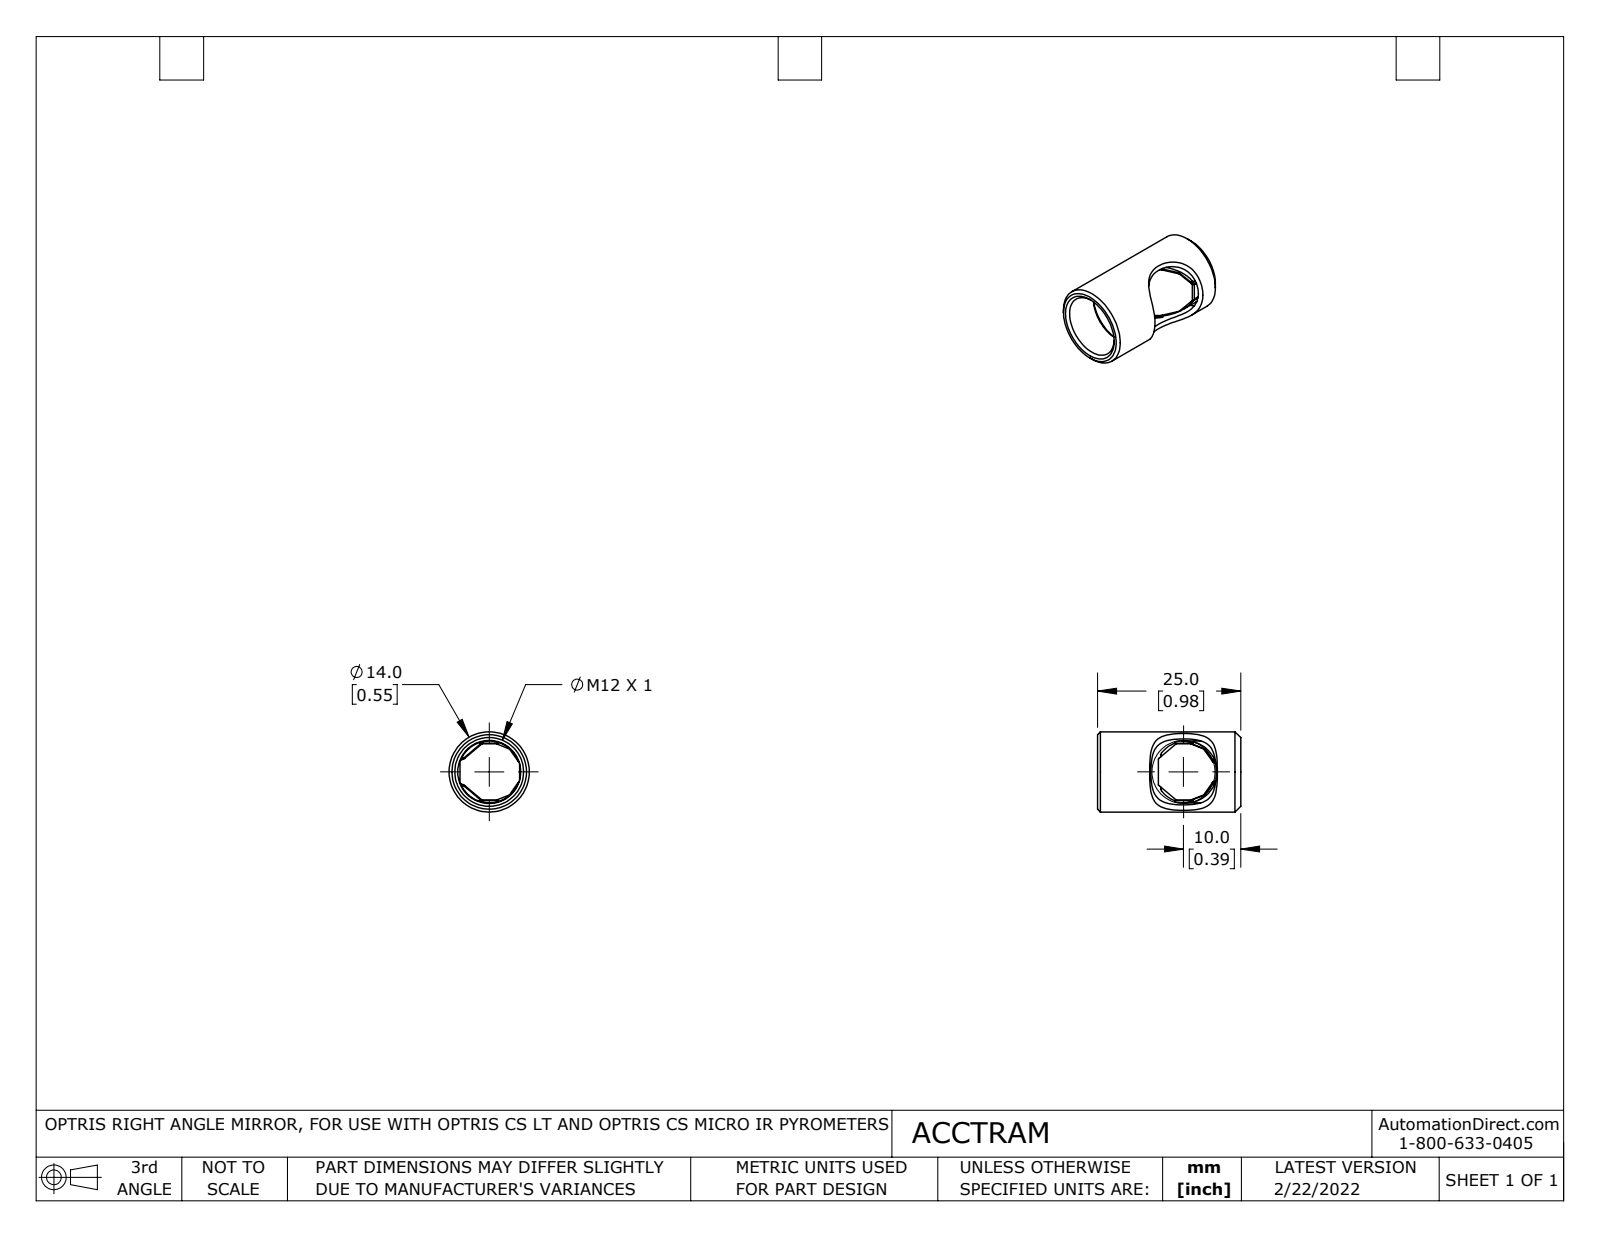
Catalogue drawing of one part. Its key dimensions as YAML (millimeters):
part_name: "ACCTRAM - Right angle mirror nc fxt"
step_written_by: "SolidWorks 2021 (AUTOMOTIVE_DESIGN)"
units: millimeters
bodies: {solids: 5, faces: 196, planar: 85, cylindrical: 48, other: 63}
overall_size: [25, 14, 14]
volume: 1800
surface_area: 3019
round_holes:
  - {diameter: 1.6, count: 2}
  - {diameter: 2.4, count: 2}
  - {diameter: 11, count: 1}
  - {diameter: 12.2, count: 1}
round_bosses_or_shafts:
  - {diameter: 3.8, count: 2}
  - {diameter: 2, count: 2}
  - {diameter: 14, count: 1}
partial_cylinders:
  - {radius: 0.5, count: 6}
  - {radius: 1.5, count: 6}
  - {radius: 0.1, count: 4}
  - {radius: 0.2, count: 4}
  - {radius: 0.3, count: 2}
  - {radius: 5.4, count: 1}
  - {radius: 6, count: 1}
face_to_face_distances: [0.3, 1.5, 1.9, 0.4, 10.1, 25, 23.5, 23.1, 1.8, 23.2]
hole_center_spacings: [3, 6]
